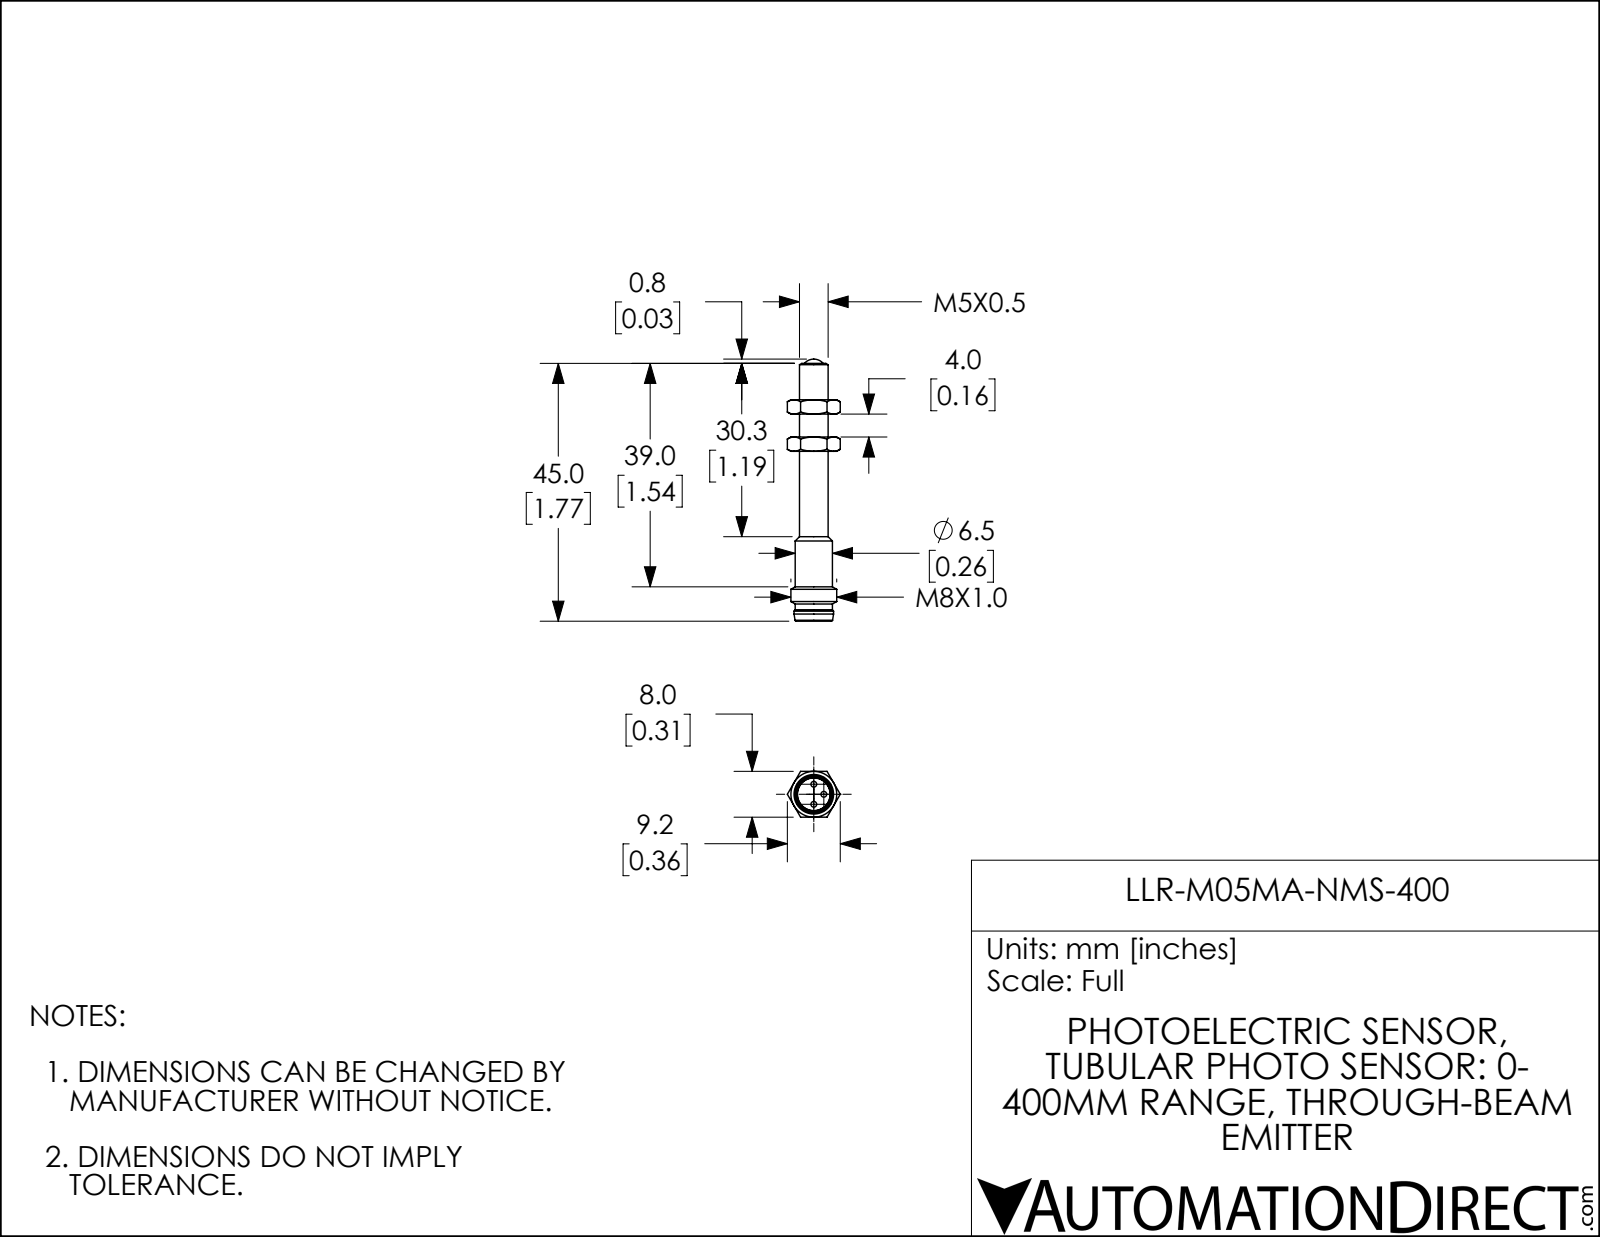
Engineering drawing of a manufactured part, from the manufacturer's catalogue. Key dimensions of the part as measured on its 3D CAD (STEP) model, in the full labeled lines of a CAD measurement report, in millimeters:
Part name (STEP PRODUCT): LLR-M05MA-NMS-400
STEP written by: SolidWorks 2018 (AUTOMOTIVE_DESIGN)
Units: millimetres
Bodies: 3 solids, 75 faces (21 planar, 14 cylindrical, 40 other)
Overall size (bounding box): 45.7 × 9.2 × 8
Volume: 1 200 mm³ · Surface area: 1 343 mm²
Round holes (diameter × count): ⌀3.6 ×1, ⌀5 ×1, ⌀5.8 ×1
Round bosses / shafts (diameter × count): ⌀1 ×3, ⌀8 ×1, ⌀6.9 ×1, ⌀6.5 ×1, ⌀5.7 ×1, ⌀3.5 ×1
Main face-to-face distances: 8, 6.5, 2.5, 9, 4, 24.7, 27.2, 31.2, 33.7, 40.1
